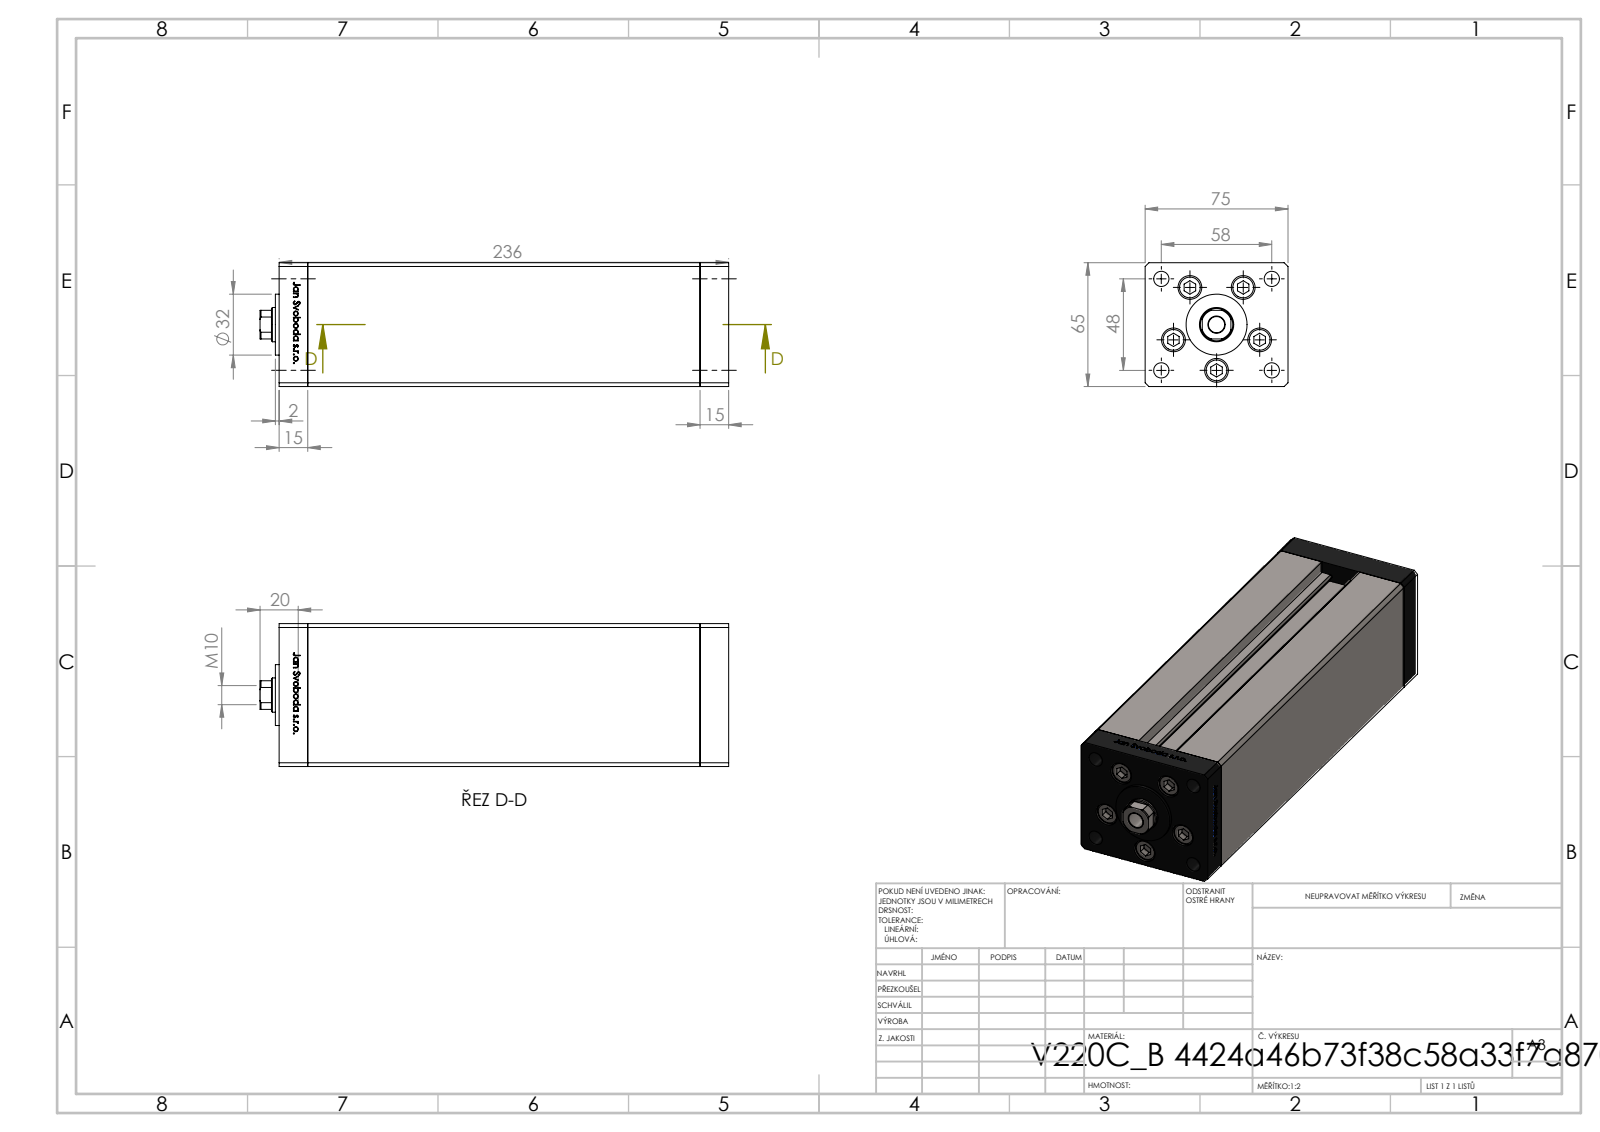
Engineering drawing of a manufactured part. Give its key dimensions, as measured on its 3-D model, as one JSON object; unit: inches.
{"part_name": "V220C BACK_B; V220C_B MIDDLE; V220C_FRONT_B; ALLEN BOLT (+1 more)", "step_written_by": "SolidWorks 2019 (CONFIG_CONTROL_DESIGN)", "units": "inches", "bodies": {"solids": 14, "faces": 1183, "planar": 462, "cylindrical": 147, "other": 574}, "overall_size": [9.685, 2.953, 2.559], "volume_in3": 61.7, "surface_area_in2": 246.9, "round_holes": [[0.354, 5], [0.492, 5], [0.315, 4], [0.079, 2], [0.518, 2], [0.335, 1], [0.709, 1]], "round_bosses_or_shafts": [[0.315, 5], [1.26, 1]], "partial_cylinders_radius": [[0.037, 2], [0.335, 1]], "face_to_face_distances": [2.953, 2.559, 0.591, 8.11, 8.701, 9.291, 2.146, 0.413, 1.033, 1.919], "hole_center_spacings": [0.945, 1.482, 0.617, 0.678, 1.091, 1.135, 1.142, 1.285]}
